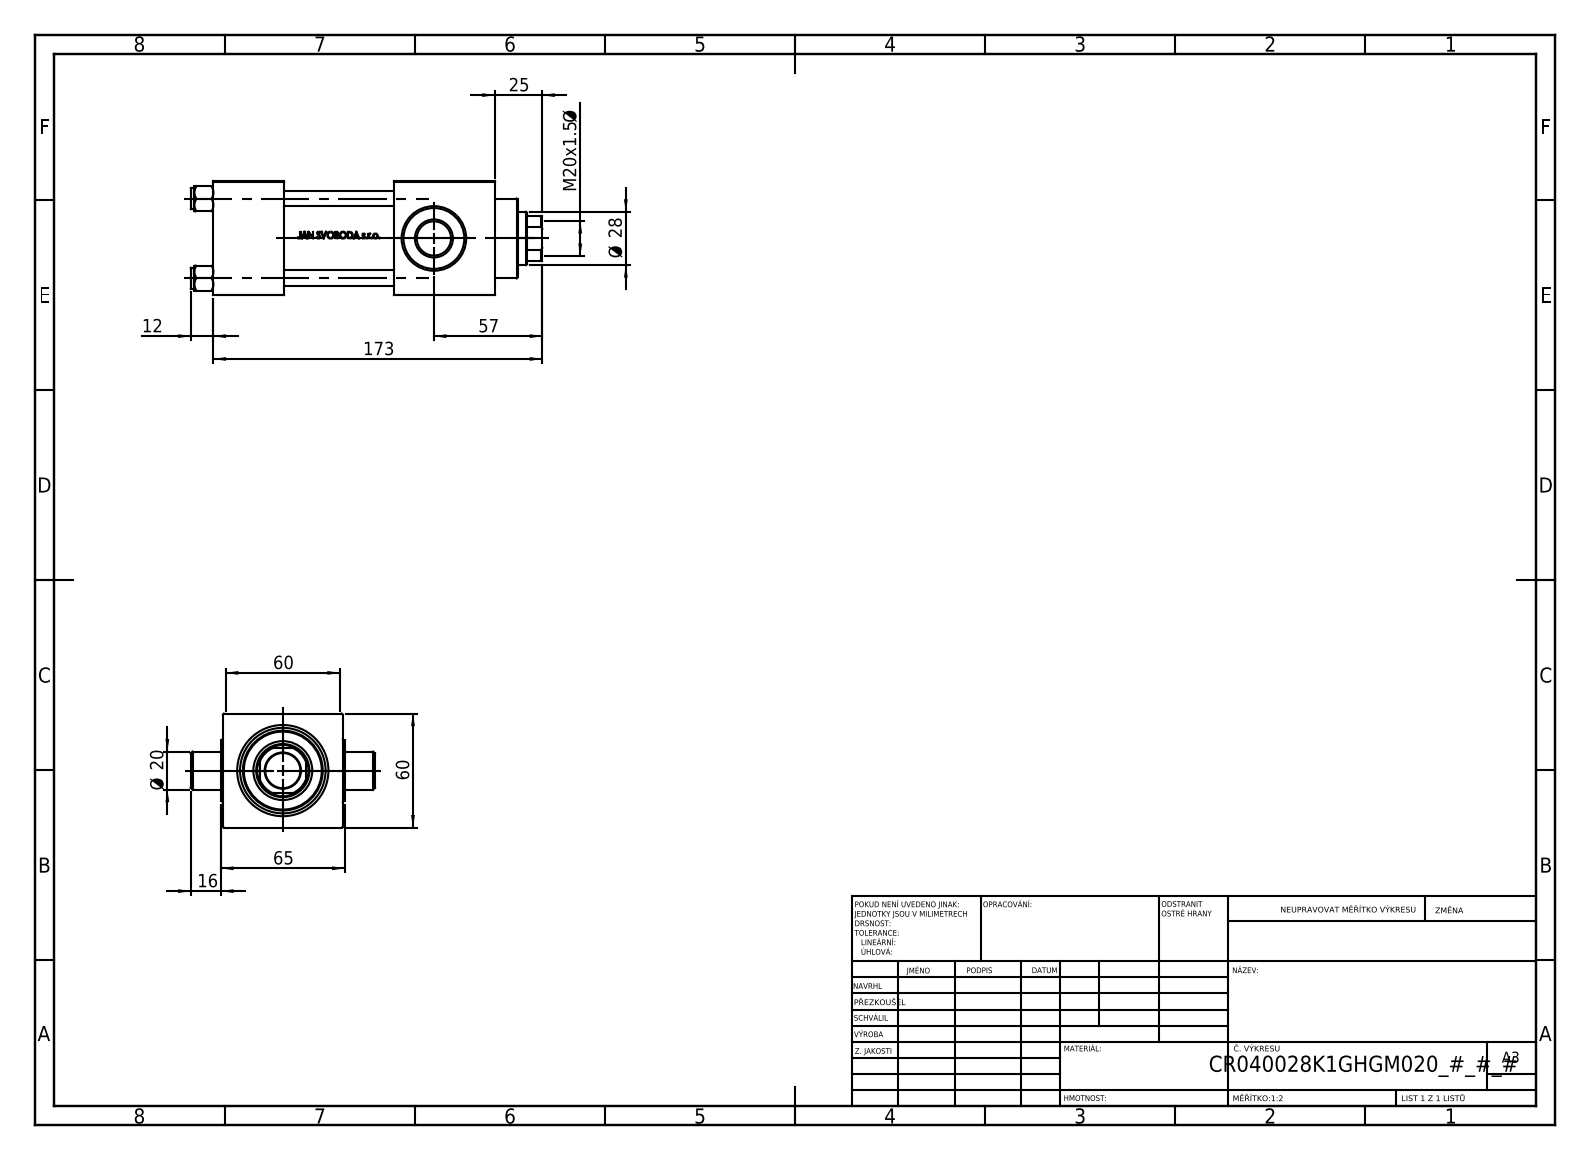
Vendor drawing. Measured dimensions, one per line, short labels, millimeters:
name: V215CR_VCP_K; NUT_M5_K; V215CR_K_Body; V215CR_K_TYCINKA (+1 more)
written by: SolidWorks 2019 (CONFIG_CONTROL_DESIGN)
unit: mm
bodies: 11 solids, 1059 faces (427 planar, 110 cylindrical, 522 other)
size: 185 × 97 × 60
volume: 454 072 mm³; area: 109 618 mm²
holes: 4× ⌀8, 1× ⌀7, 1× ⌀18.5, 1× ⌀28, 1× ⌀31, 1× ⌀40, 1× ⌀45
bosses: 4× ⌀11, 1× ⌀46, 1× ⌀42, 1× ⌀20
rounds: 1× R13.5
face distances: 60, 1.5, 61.5, 37, 63, 95, 58, 148, 111, 53
hole spacings: 29.49, 41.7, 58.97
